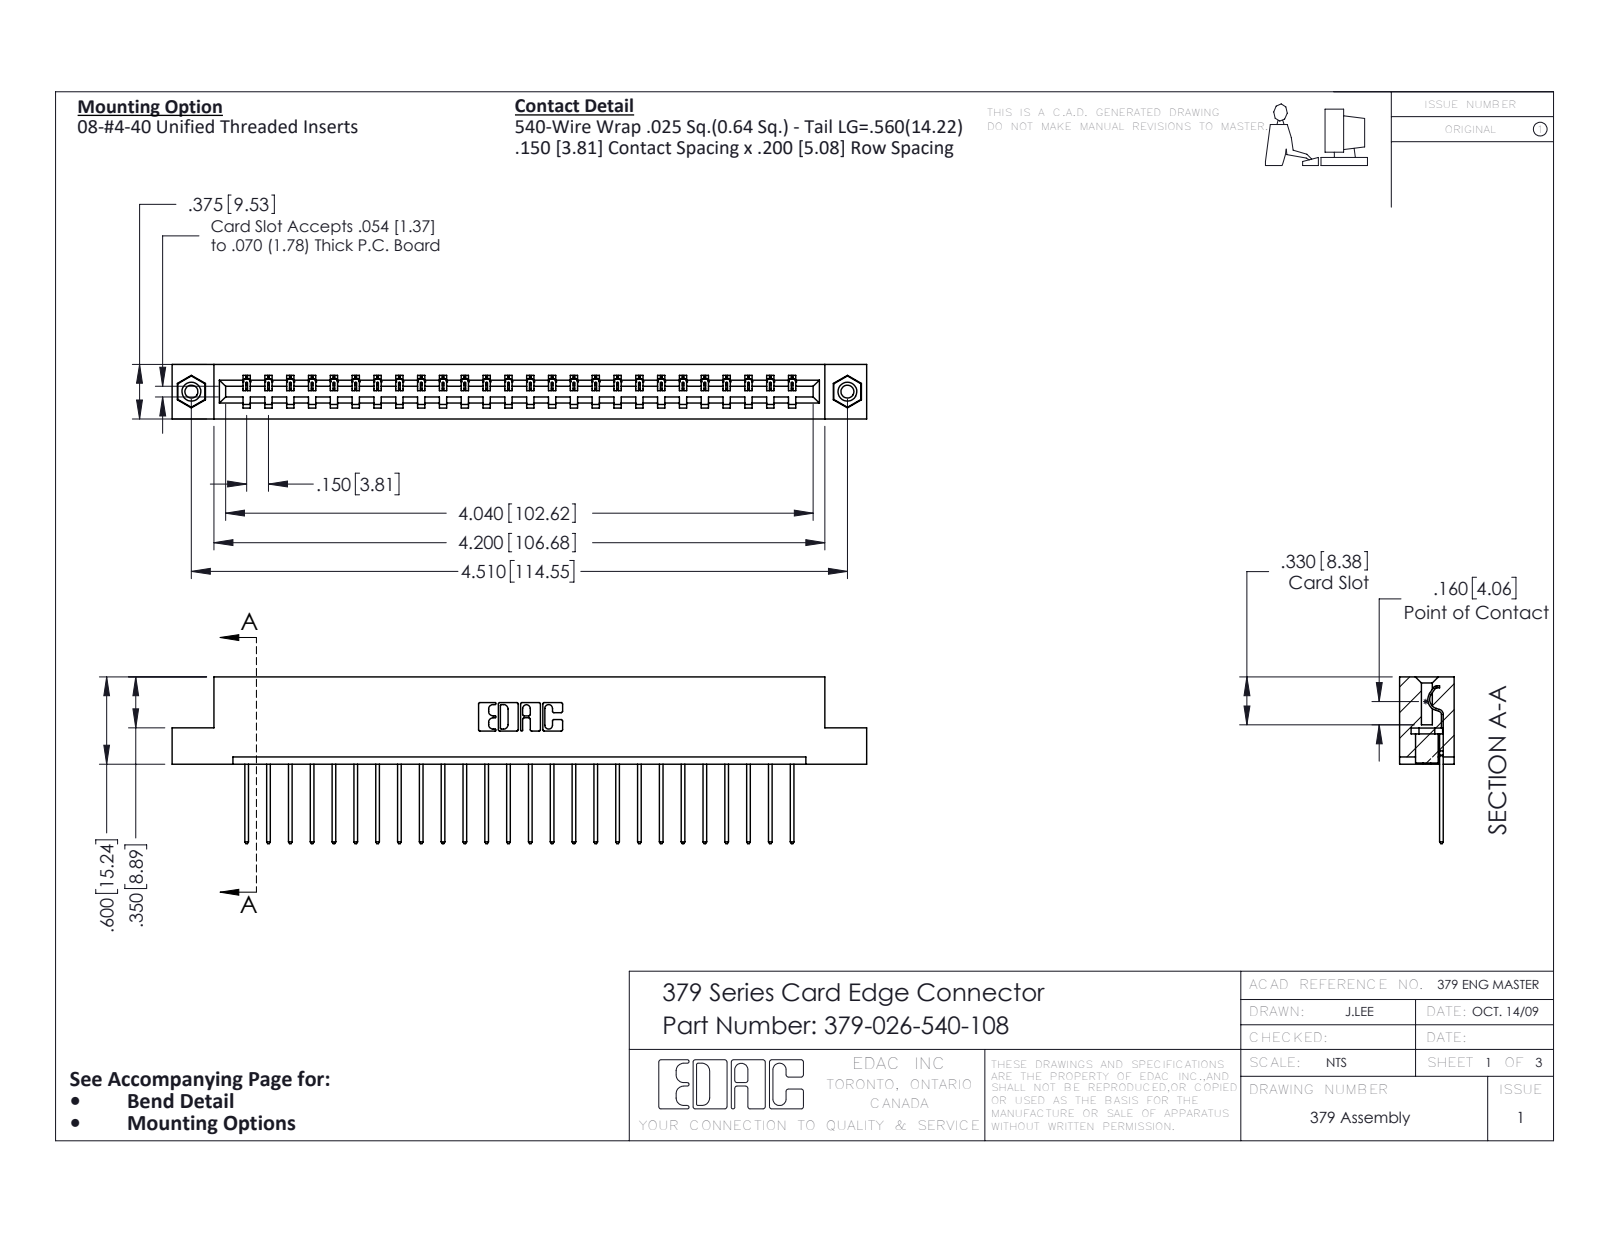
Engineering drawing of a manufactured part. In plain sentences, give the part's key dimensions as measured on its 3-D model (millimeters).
The part is named "345-292-001_345-293-140; 379 Part_Flush - .156 Dia - TI; 345-250-001_345-250-003-102; 379-026-540-108". Its 3-D file was written by "SolidWorks 2016 (CONFIG_CONTROL_DESIGN)". It is 29 solids with 1682 faces: 1194 planar, 472 cylindrical and 16 other. Overall it measures 121.3 by 29.1 by 9.5 millimeters. Its volume is 12 600 cubic millimeters and its surface area 13 080 square millimeters. Round holes: 2 of diameter 2.3, 2 of diameter 3.2, 2 of diameter 4. Round bosses or shafts: 2 of diameter 3.9. Partial cylindrical surfaces (rounded edges, fillets, slot ends): 52 of radius 0.2, 52 of radius 0.3, 22 of radius 0.3, 6 of radius 0.2, 6 of radius 0.8, 3 of radius 0.7, 1 of radius 0.4, 1 of radius 0.6. The main face-to-face distances are 7.6, 1.9, 9.5, 5.7, 15.2, 7, 5.1, 2.5, 0.6, 3.8. The hole center spacings are 114.6.
